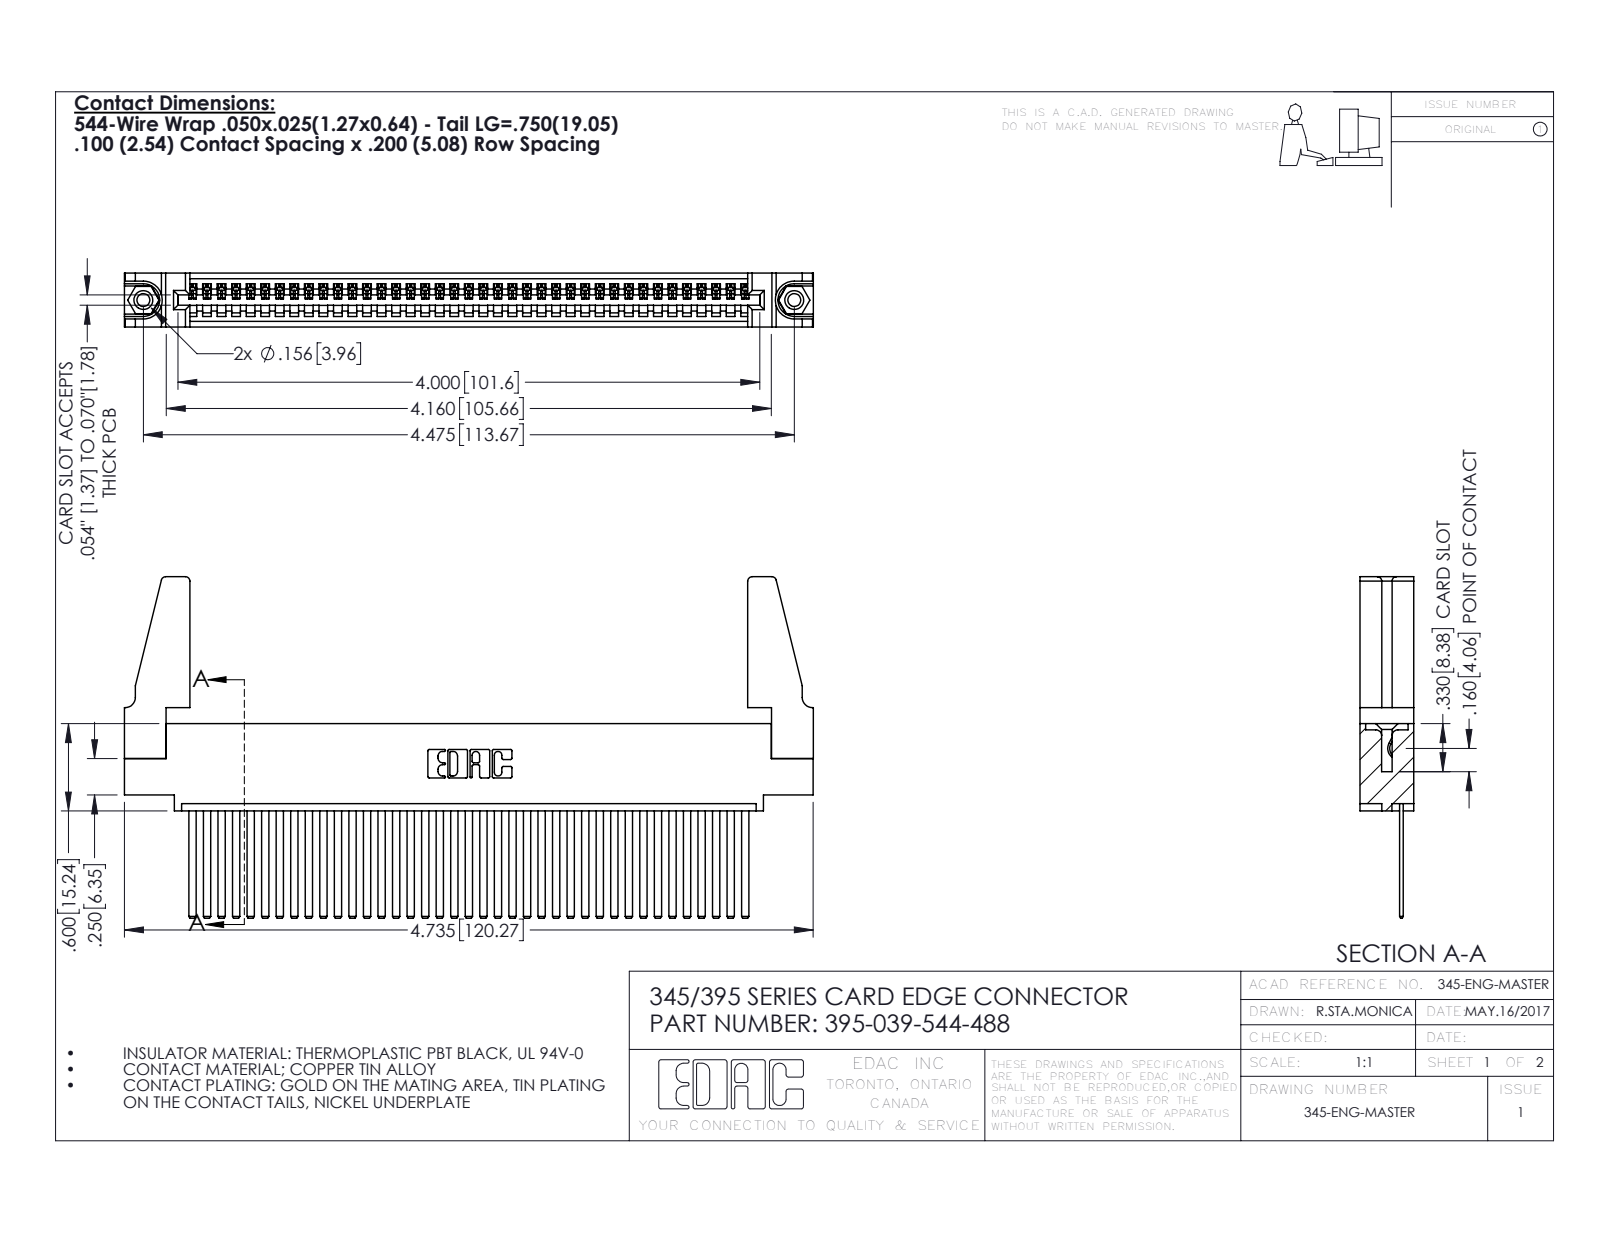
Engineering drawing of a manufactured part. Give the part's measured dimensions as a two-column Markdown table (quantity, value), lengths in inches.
| quantity | value |
| --- | --- |
| part name | 345 Part_0.110 Offset - 0.156 Dia-TH; 345-220-078_345-220-088; 345-250-001_345-250-001-102; 395-039-544-488 (+1 more) |
| STEP written by | SolidWorks 2016 (CONFIG_CONTROL_DESIGN) |
| units | inches |
| bodies | 44 solids, 2282 faces (1560 planar, 706 cylindrical, 16 other) |
| overall size | 4.736 × 2.347 × 0.37 |
| volume | 0.917 in³ |
| surface area | 31.28 in² |
| round holes (diameter × count) | 0.089 × 2, 0.125 × 2, 0.156 × 2, 0.064 × 1 |
| round bosses / shafts (diameter × count) | 0.155 × 2 |
| partial cylindrical surfaces (radius × count) | 0.006 × 78, 0.01 × 22, 0.03 × 8, 0.007 × 6, 0.031 × 6, 0.026 × 3, 0.031 × 2, 0.04 × 2 |
| main face-to-face distances | 0.072, 0.298, 0.098, 0.272, 0.025, 0.37, 0.2, 0.225, 0.149, 0.072 |
| hole center spacings | 0.27, 4.239, 4.475 |
